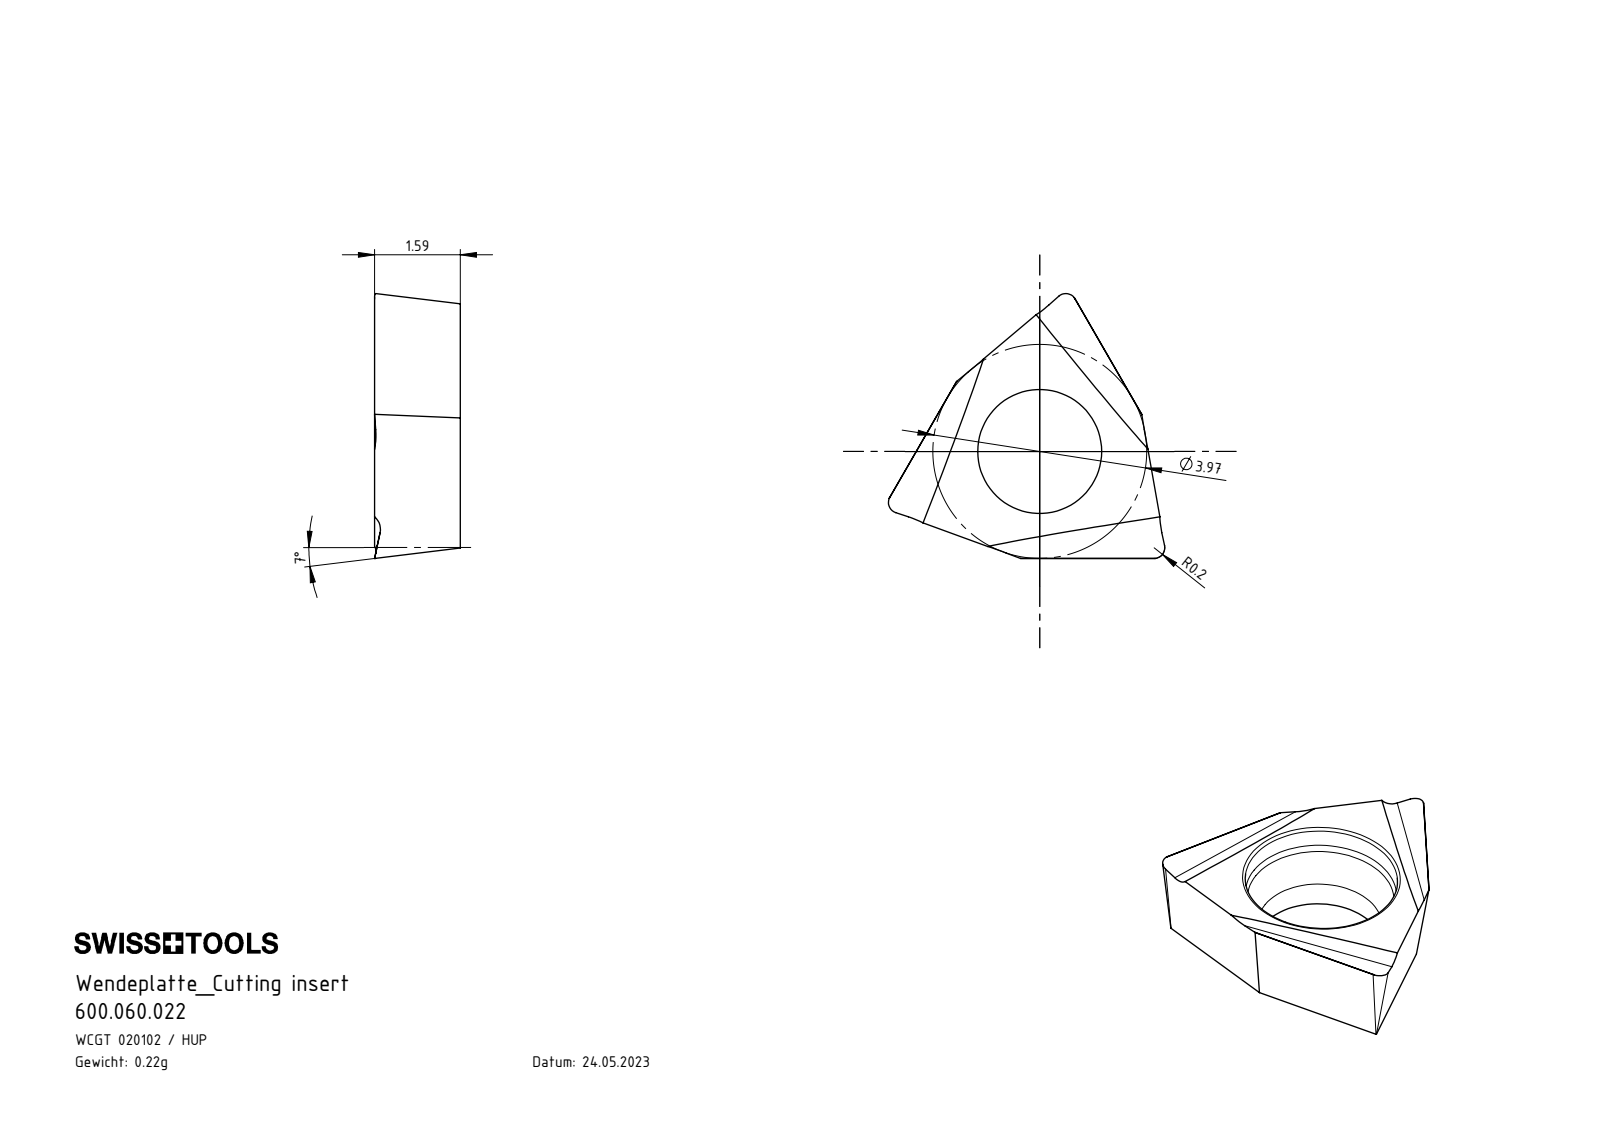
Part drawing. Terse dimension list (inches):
name: 600.060.022
written by: SolidWorks 2022 (AUTOMOTIVE_DESIGN)
unit: in
bodies: 1 solid, 31 faces (14 planar, 5 cylindrical, 12 other)
size: 0.202 × 0.194 × 0.063
volume: 0.001 in³; area: 0.087 in²
holes: 1× ⌀0.091
rounds: 3× R0.012
face distances: 0.063
